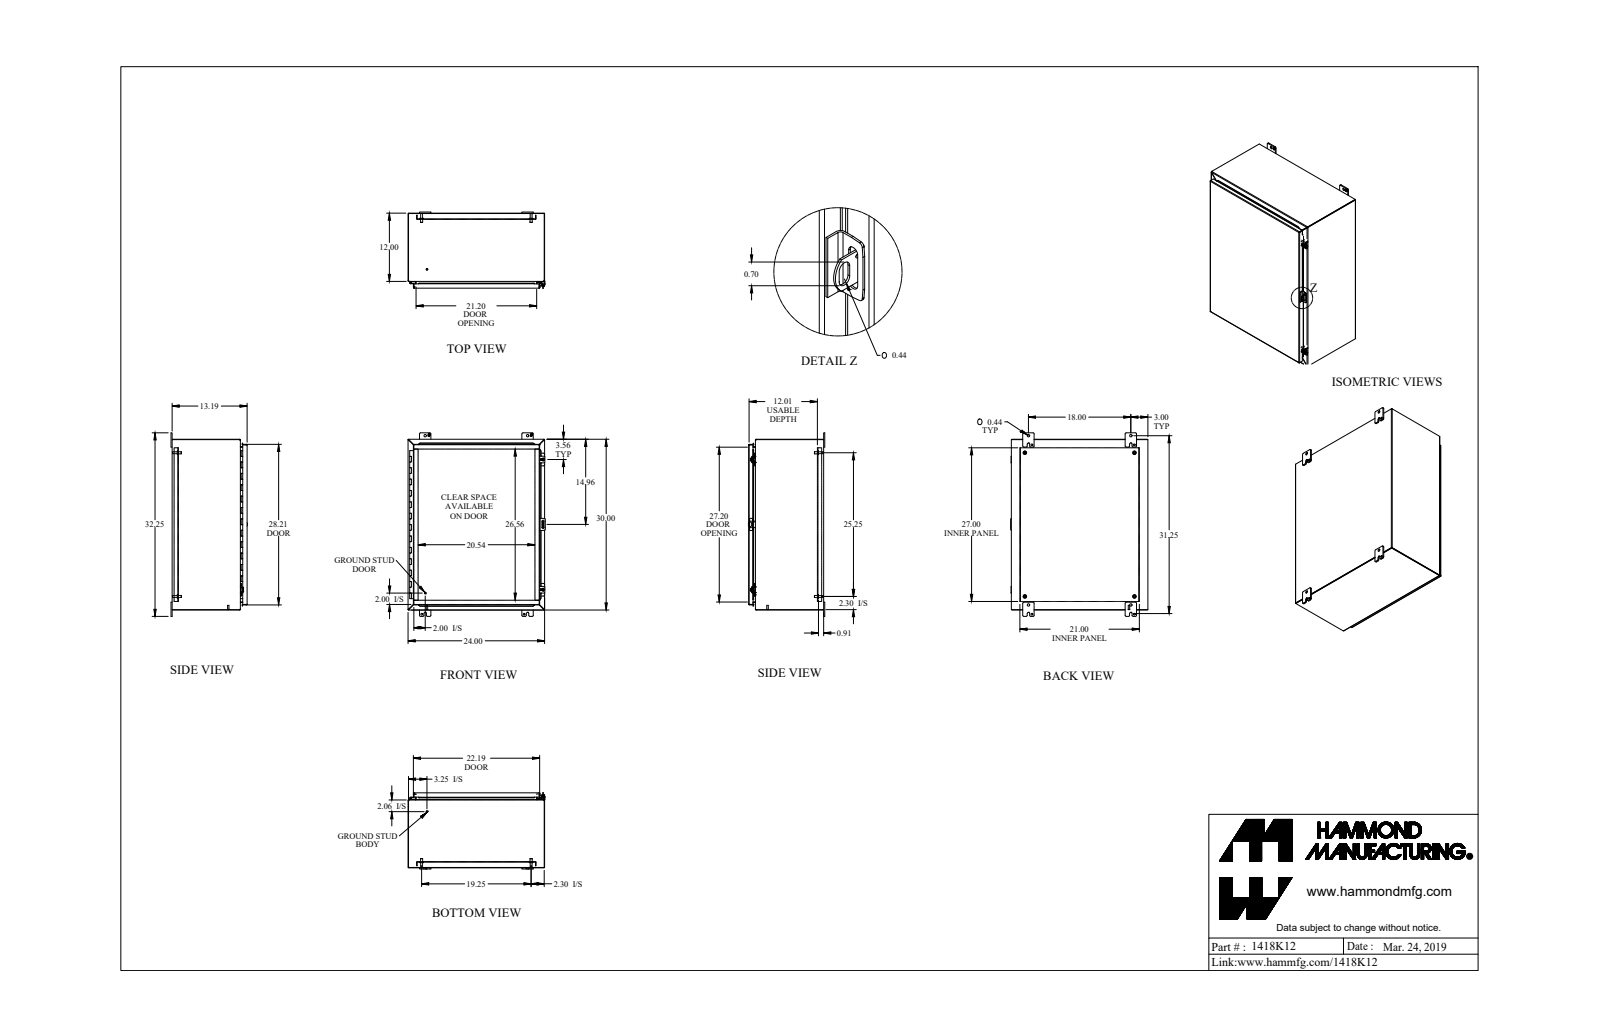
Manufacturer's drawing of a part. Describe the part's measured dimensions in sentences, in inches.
The part is named "1418K12_Default". Its 3-D file was written by "SolidWorks 2019 (CONFIG_CONTROL_DESIGN)". It is 40 solids with 1203 faces: 723 planar, 404 cylindrical and 76 other. Overall it measures 32.25 by 24.125 by 13.437 inches. Its volume is 294.2 cubic inches and its surface area 7 681 square inches. Round holes: 4 of diameter 0.313, 4 of diameter 0.437, 4 of diameter 0.5, 2 of diameter 0.213, 2 of diameter 0.265, 2 of diameter 0.307, 2 of diameter 0.375, 1 of diameter 0.125, 1 of diameter 0.187, 1 of diameter 0.445, 1 of diameter 0.445. Round bosses or shafts: 4 of diameter 0.65, 4 of diameter 0.375, 4 of diameter 0.33, 2 of diameter 1, 2 of diameter 0.5, 2 of diameter 0.39, 2 of diameter 0.281, 2 of diameter 0.25. Partial cylindrical surfaces (rounded edges, fillets, slot ends): 26 of radius 0.188, 22 of radius 0.036, 22 of radius 0.108, 13 of radius 0.048, 13 of radius 0.143, 12 of radius 0.25, 8 of radius 0.04, 8 of radius 0.218. The main face-to-face distances are 0.072, 13.113, 13.041, 23.928, 13.185, 0.937, 0.095, 1.009, 29.928, 12.081. The hole center spacings are 1.736, 18, 29.75, 34.772, 19.25, 31.751, 1.625, 2.434.
